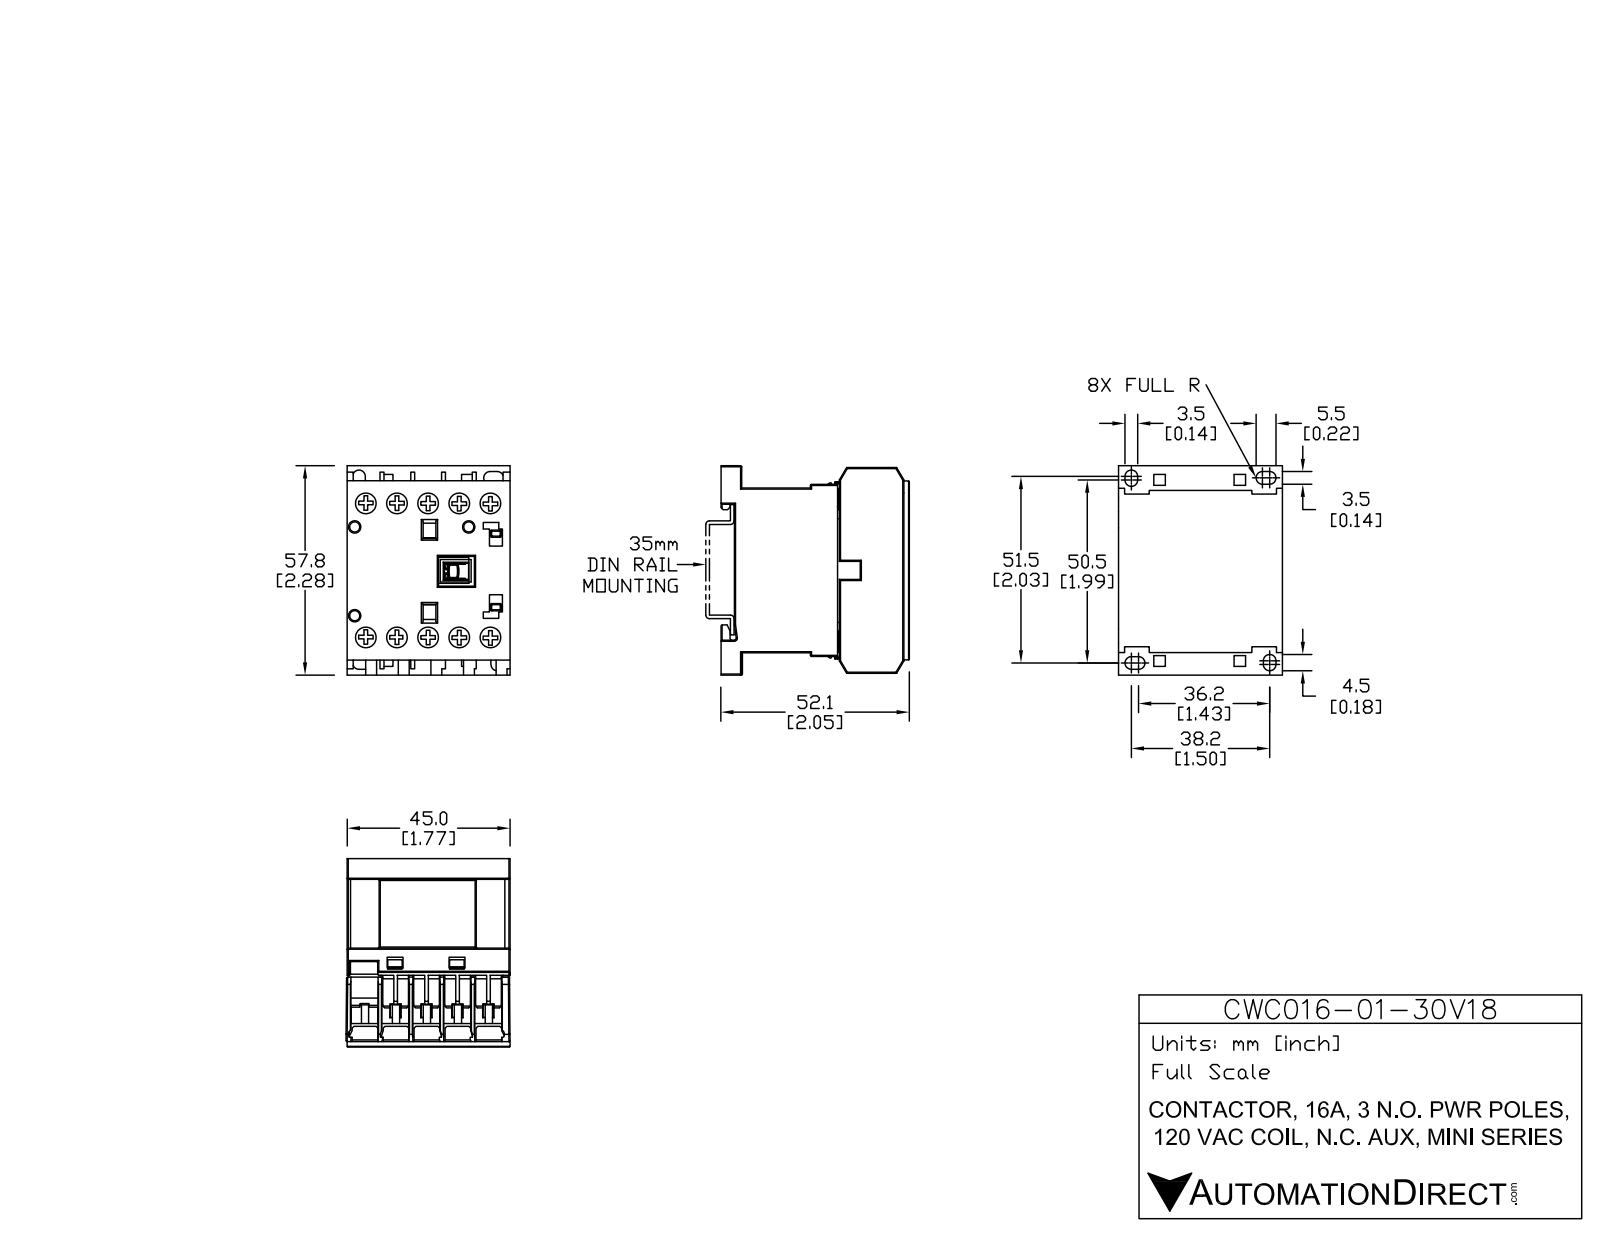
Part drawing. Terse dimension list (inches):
name: CWC16-01-30V18
written by: SolidWorks 2013 (AUTOMOTIVE_DESIGN)
unit: in
bodies: 15 solids, 535 faces (445 planar, 90 cylindrical, 0 other)
size: 2.285 × 2.052 × 1.801
volume: 5.927 in³; area: 47.18 in²
holes: 10× ⌀0.244, 3× ⌀0.11
bosses: 10× ⌀0.232
rounds: 20× R0.012, 6× R0.068, 2× R0.068, 1× R0.013, 1× R0.017, 1× R0.022
face distances: 0.325, 1.791, 0.049, 0.65, 0.374, 0.217, 0.699, 0.202, 0.419, 0.276
hole spacings: 0.337, 1.494, 0.673, 1.603, 1.455, 1.01, 1.771, 0.272
